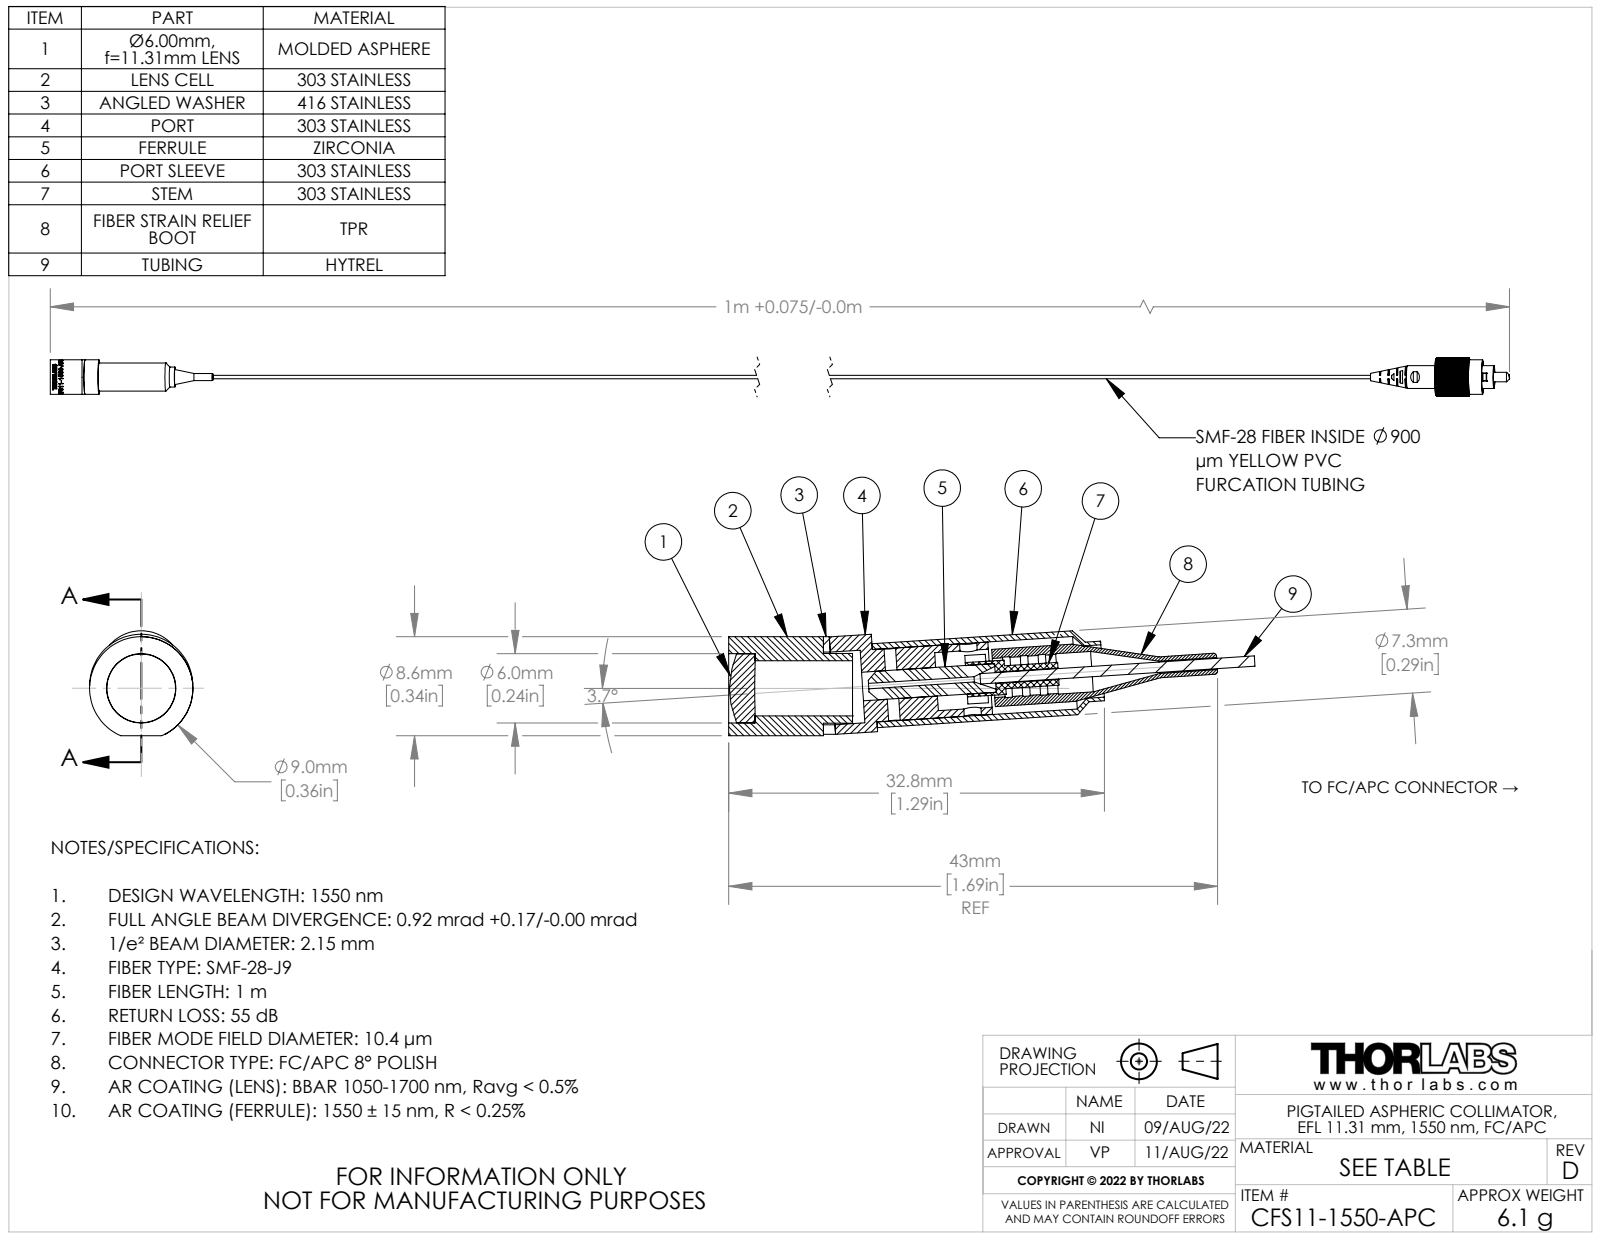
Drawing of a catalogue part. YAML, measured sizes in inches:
part_name: "17367-E0W"
step_written_by: "SolidWorks 2018 (CONFIG_CONTROL_DESIGN)"
units: inches
bodies: {solids: 12, faces: 520, planar: 252, cylindrical: 222, other: 46}
overall_size: [40.6, 2.934, 0.393]
volume: 0.158
surface_area: 12.2
round_holes:
  - {diameter: 0.04, count: 2}
  - {diameter: 0.059, count: 2}
  - {diameter: 0.2, count: 2}
  - {diameter: 0.25, count: 2}
  - {diameter: 0.018, count: 1}
  - {diameter: 0.039, count: 1}
  - {diameter: 0.042, count: 1}
  - {diameter: 0.055, count: 1}
  - {diameter: 0.098, count: 1}
  - {diameter: 0.098, count: 1}
  - {diameter: 0.119, count: 1}
  - {diameter: 0.12, count: 1}
round_bosses_or_shafts:
  - {diameter: 0.355, count: 2}
  - {diameter: 0.235, count: 2}
  - {diameter: 0.098, count: 2}
  - {diameter: 0.354, count: 1}
  - {diameter: 0.289, count: 1}
  - {diameter: 0.28, count: 1}
  - {diameter: 0.249, count: 1}
  - {diameter: 0.24, count: 1}
partial_cylinders:
  - {radius: 0.089, count: 1}
  - {radius: 0.117, count: 1}
  - {radius: 0.197, count: 1}
face_to_face_distances: [0.267, 39.728, 0.267, 39.521, 0.145, 0.04, 0.326, 39.768, 39.583, 39.623]
hole_center_spacings: [0.02, 0.02, 0.27]
